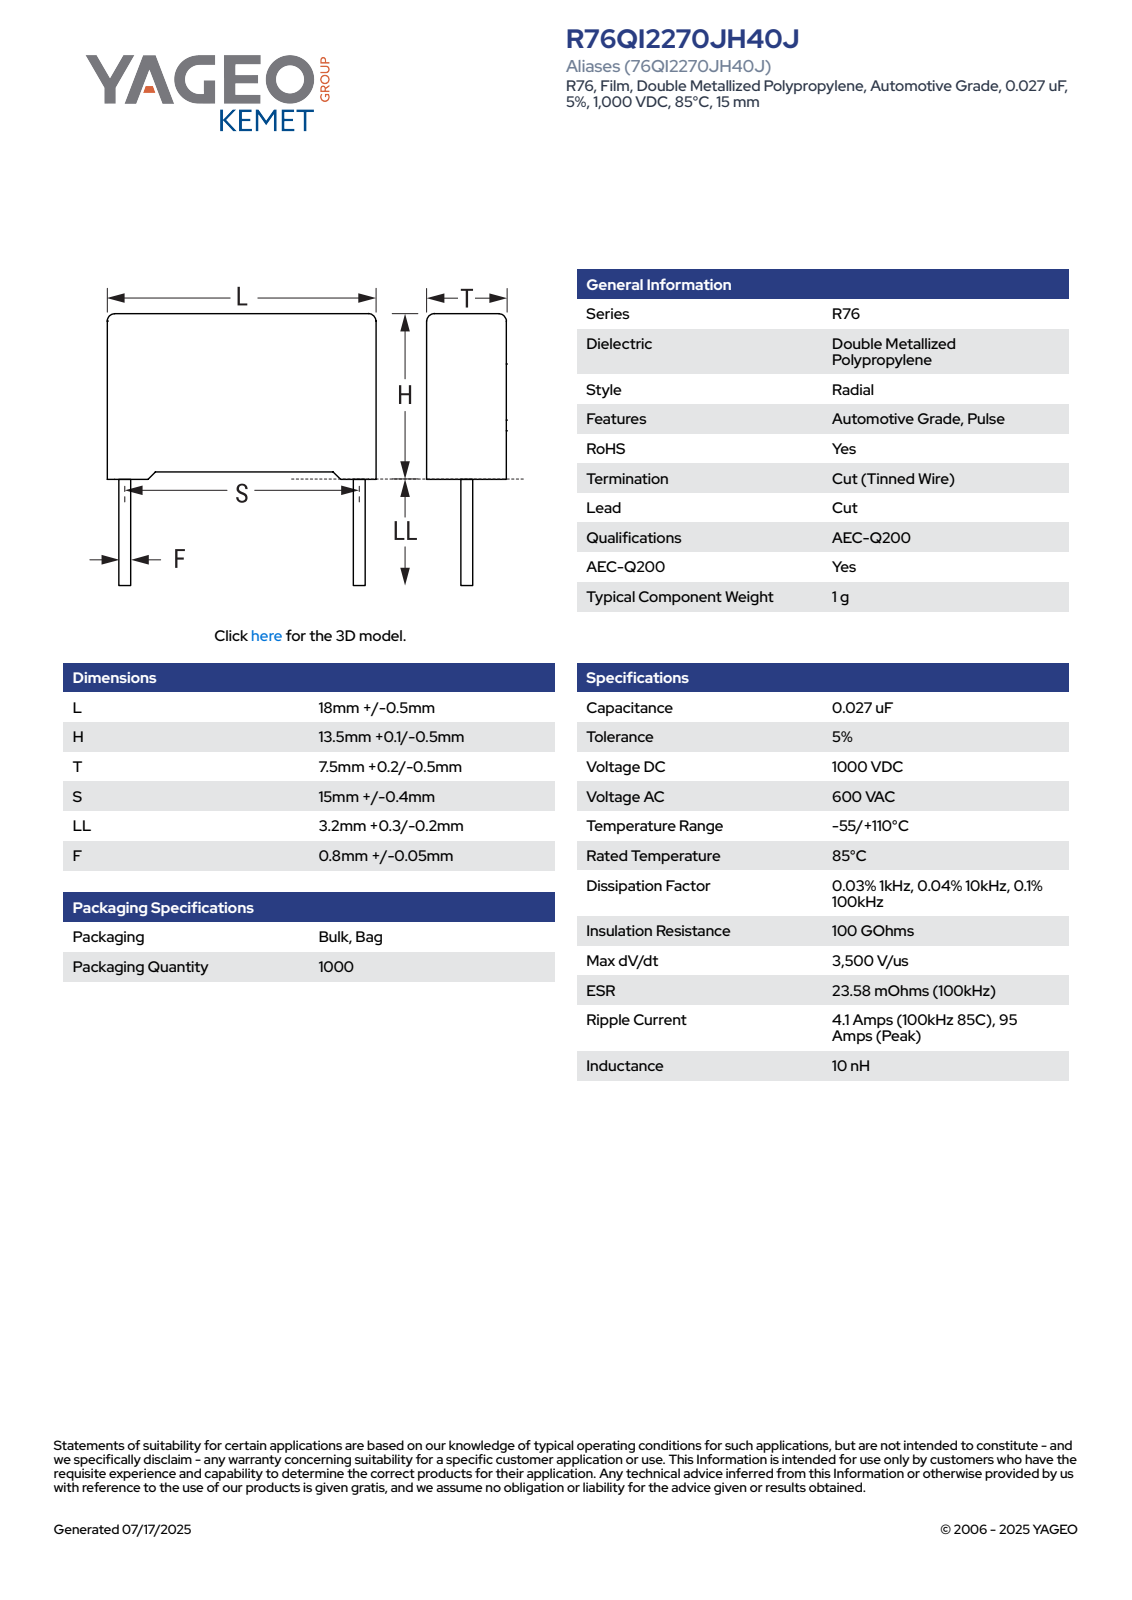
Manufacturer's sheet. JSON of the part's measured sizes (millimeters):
{"part_name": "CFR_RB2_18X13.5X7.5_L18.5H13.6T7.7S15LL3.5F0.85", "step_written_by": "SolidWorks 2021 (AUTOMOTIVE_DESIGN)", "units": "millimeters", "bodies": {"solids": 4, "faces": 85, "planar": 77, "cylindrical": 8, "other": 0}, "overall_size": [18.5, 17.1, 7.71], "volume_mm3": 1849, "surface_area_mm2": 1049, "round_bosses_or_shafts": [[0.85, 2]], "partial_cylinders_radius": [[0.5, 4]], "face_to_face_distances": [7.7, 12.85, 18.5, 0.62, 0.75, 13.6, 7.08, 0.47, 13.13, 17.88]}
